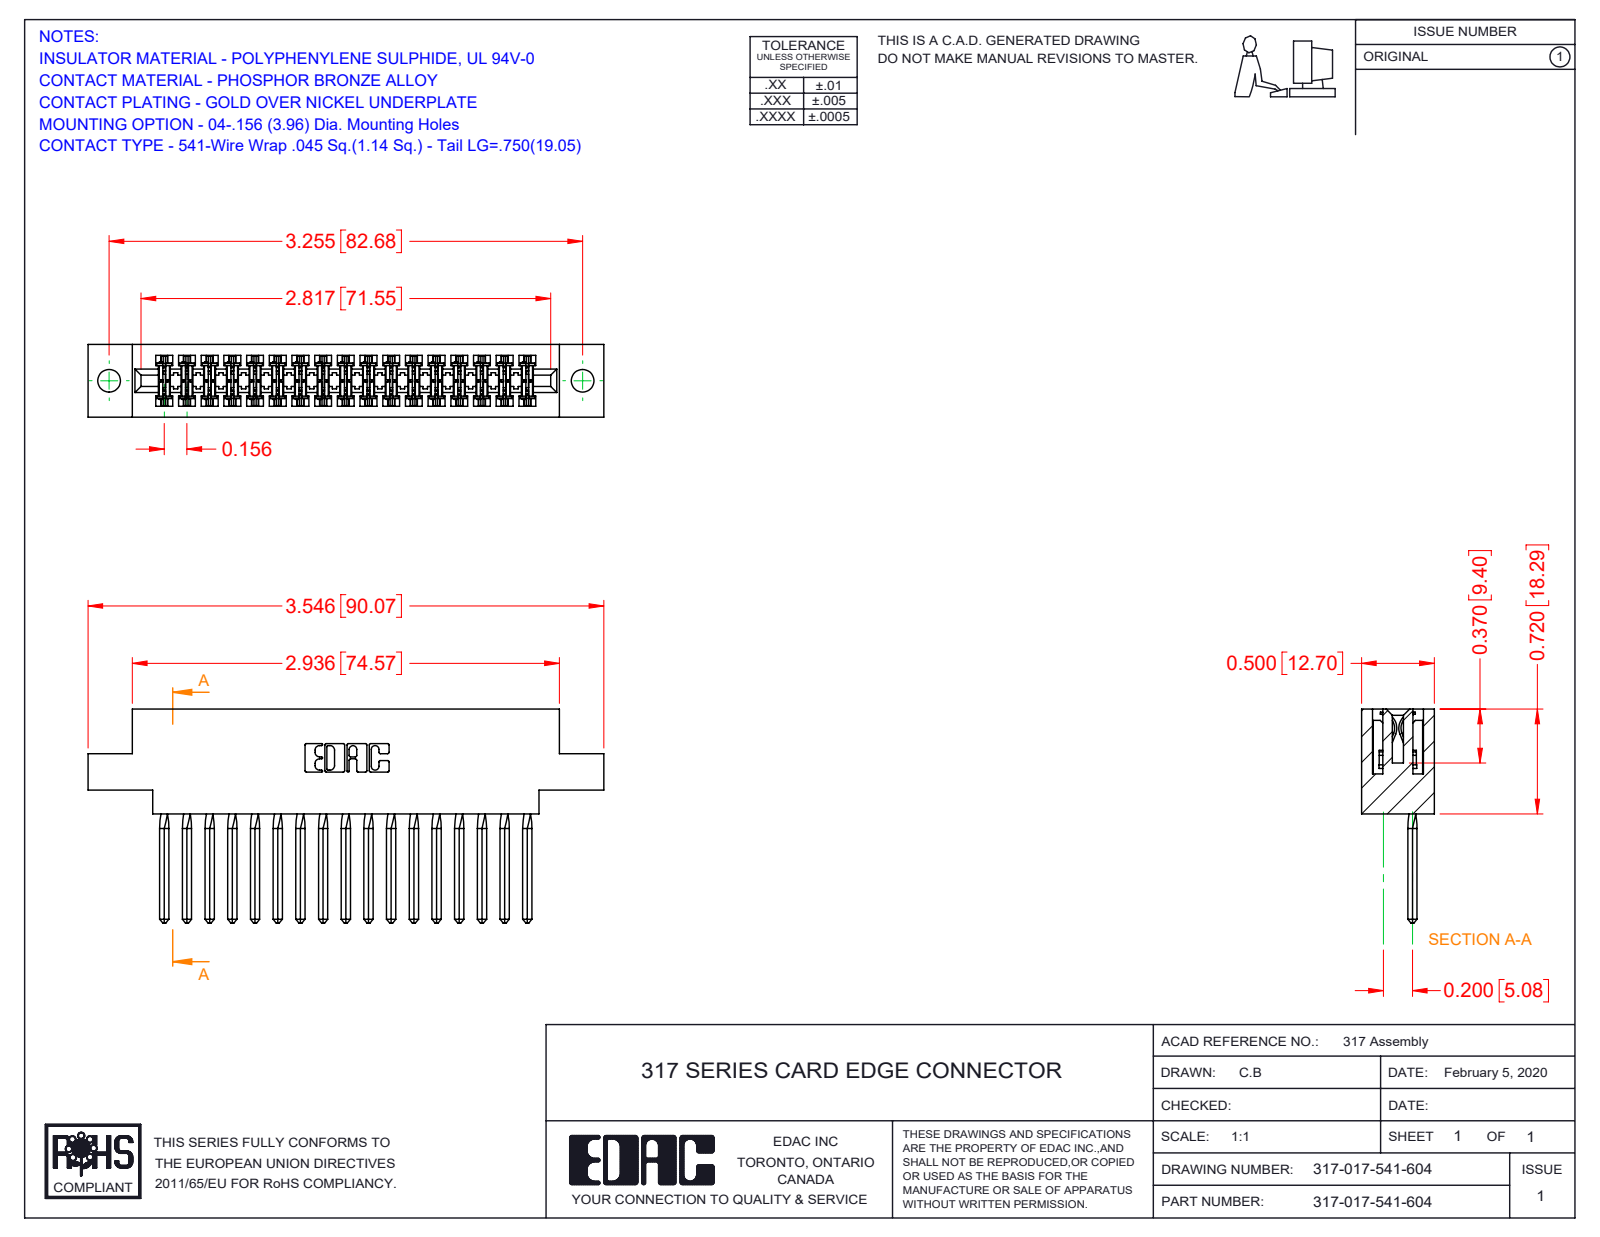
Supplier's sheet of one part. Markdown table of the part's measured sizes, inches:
| quantity | value |
| --- | --- |
| part name | 317 Part_.156 Dia - TH; 317-290-002_541; 317-017-541-604 |
| STEP written by | SolidWorks 2016 (CONFIG_CONTROL_DESIGN) |
| units | inches |
| bodies | 18 solids, 2686 faces (2166 planar, 452 cylindrical, 68 other) |
| overall size | 3.546 × 1.47 × 0.5 |
| volume | 0.839 in³ |
| surface area | 28.54 in² |
| round holes (diameter × count) | 0.156 × 2 |
| partial cylindrical surfaces (radius × count) | 0.015 × 34, 0.01 × 22, 0.007 × 6, 0.031 × 6, 0.026 × 3, 0.095 × 2, 0.1 × 2, 0.11 × 2 |
| main face-to-face distances | 0.5, 0.075, 0.425, 0.11, 0.35, 0.22, 0.195, 0.772, 0.72, 0.065 |
| hole center spacings | 3.255 |
